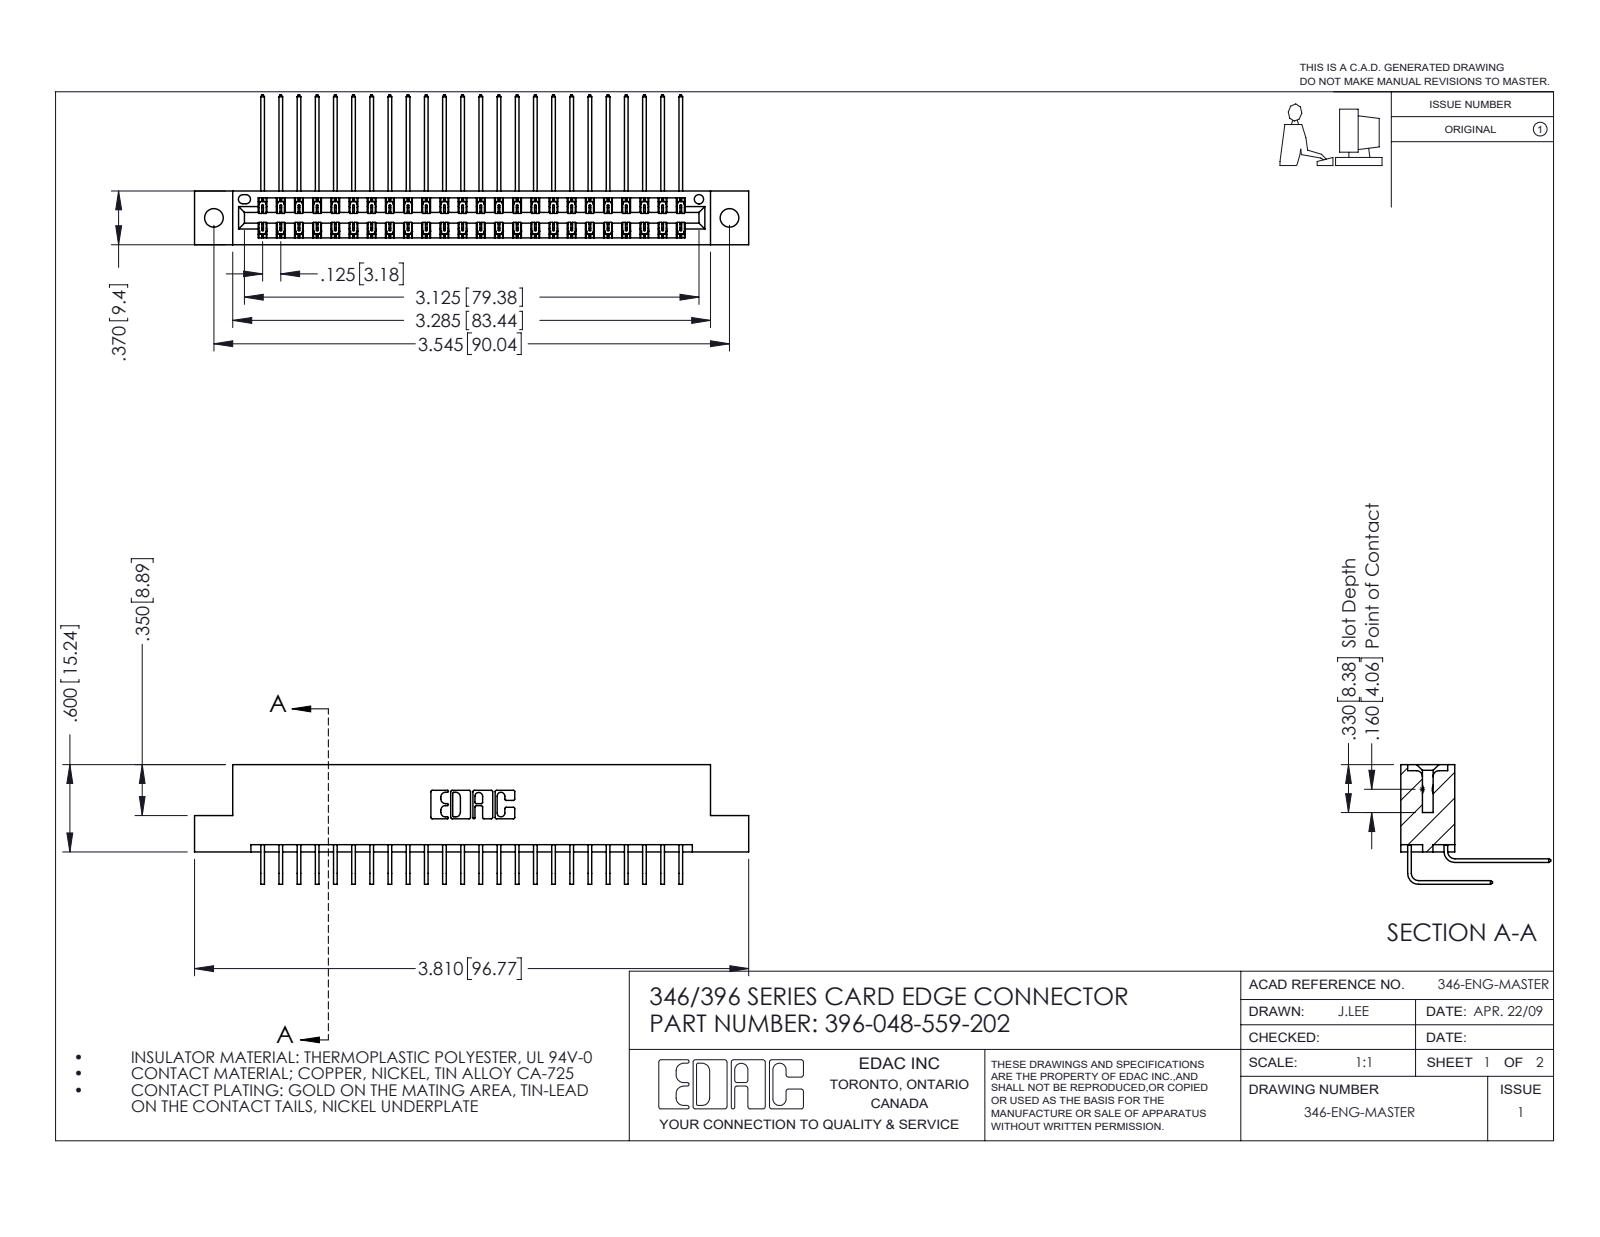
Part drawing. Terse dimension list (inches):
name: 345-292-001_558 559 Tail - 1; 396-048-559-202; 345-292-001_559 Tail - 2; 346 Part_Flush Mounting Lugs - 0.128 Dia
written by: SolidWorks 2016 (CONFIG_CONTROL_DESIGN)
unit: in
bodies: 49 solids, 2714 faces (1852 planar, 862 cylindrical, 0 other)
size: 3.81 × 1.03 × 0.823
volume: 0.582 in³; area: 21.52 in²
holes: 2× ⌀0.128, 1× ⌀0.064
rounds: 72× R0.006, 22× R0.01, 6× R0.007, 6× R0.031, 3× R0.026, 2× R0.014, 2× R0.022, 2× R0.024
face distances: 0.048, 0.322, 0.025, 0.25, 0.37, 0.072, 0.298, 0.275, 0.148, 0.222
hole spacings: 0.246, 3.337, 3.545
